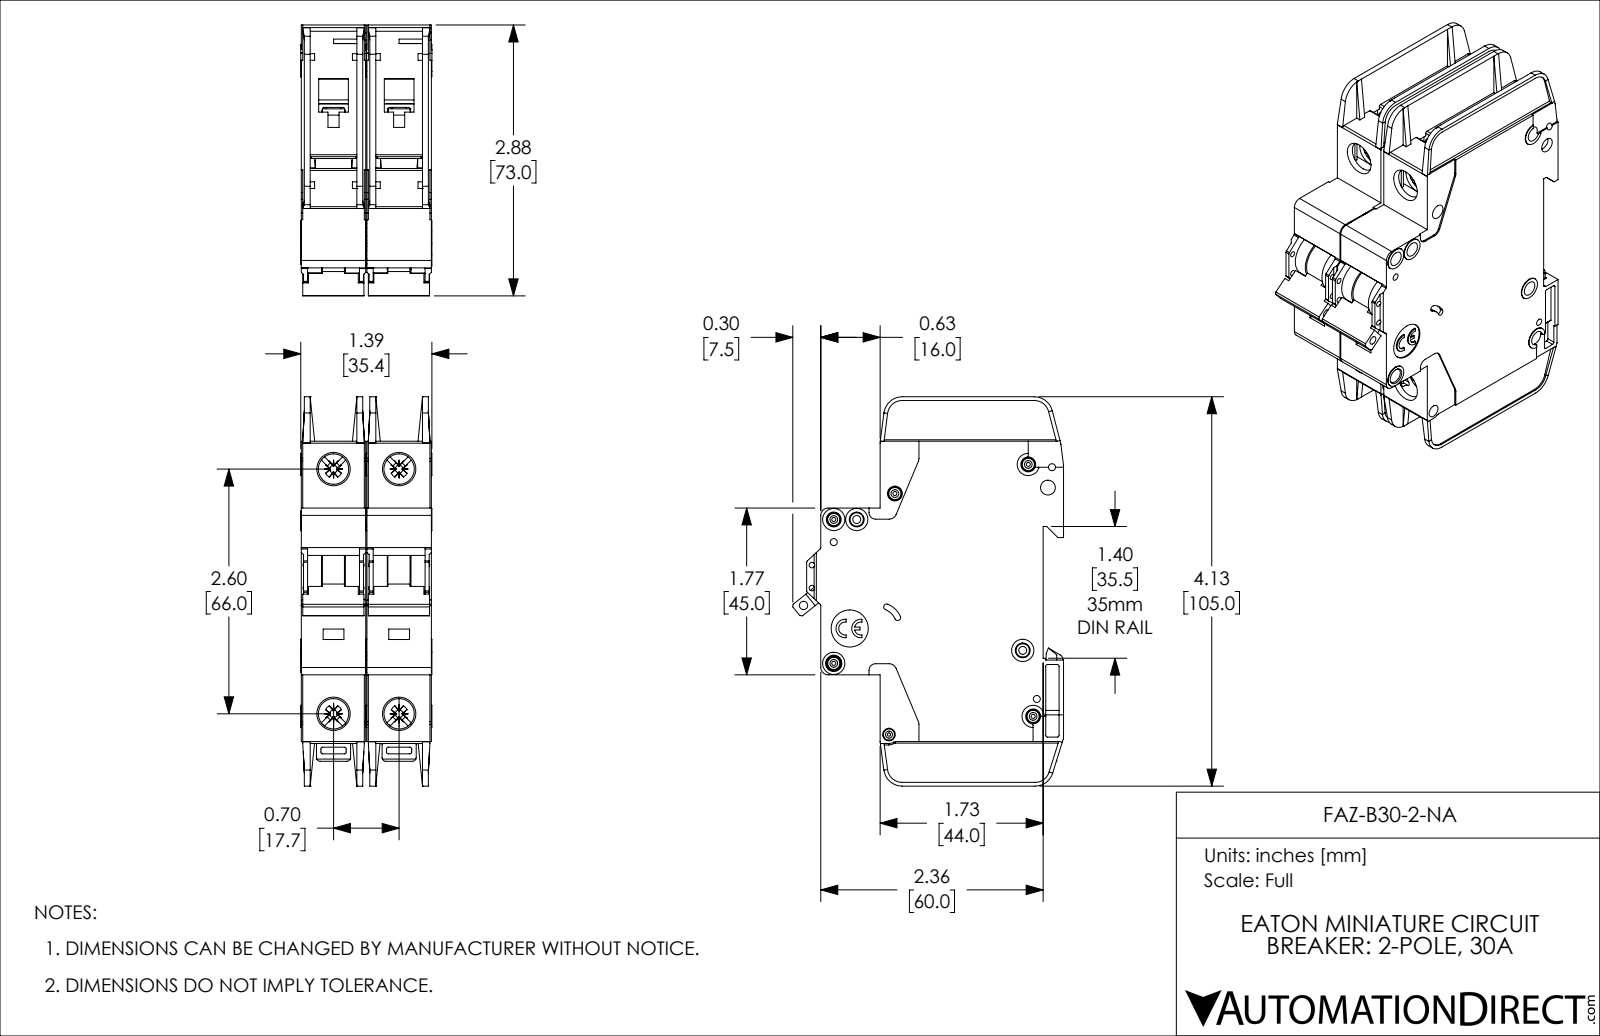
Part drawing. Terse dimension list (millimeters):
name: FAZ-B30-2-NA
written by: SolidWorks 2019 (AUTOMOTIVE_DESIGN)
unit: mm
bodies: 2 solids, 2254 faces (1342 planar, 714 cylindrical, 198 other)
size: 105 × 73.1 × 35.4
volume: 153 500 mm³; area: 52 910 mm²
holes: 8× ⌀4, 5× ⌀1.1, 4× ⌀1.9, 4× ⌀8.2, 2× ⌀1.5, 2× ⌀2.2, 1× ⌀0.9, 1× ⌀2.3, 1× ⌀2.5, 1× ⌀3.4, 1× ⌀10
bosses: 5× ⌀3.3, 4× ⌀6, 3× ⌀3, 2× ⌀2.5
rounds: 57× R0.5, 20× R0.4, 14× R1, 10× R2, 8× R1.1, 5× R0.2, 5× R5, 4× R0.3
face distances: 17.7, 1.2, 17.4, 15, 2.4, 16.2, 13.8, 35.1, 18.9, 16.5
hole spacings: 6.2, 13.6, 17.7, 22.1, 66, 68.3, 4.8, 5.1
